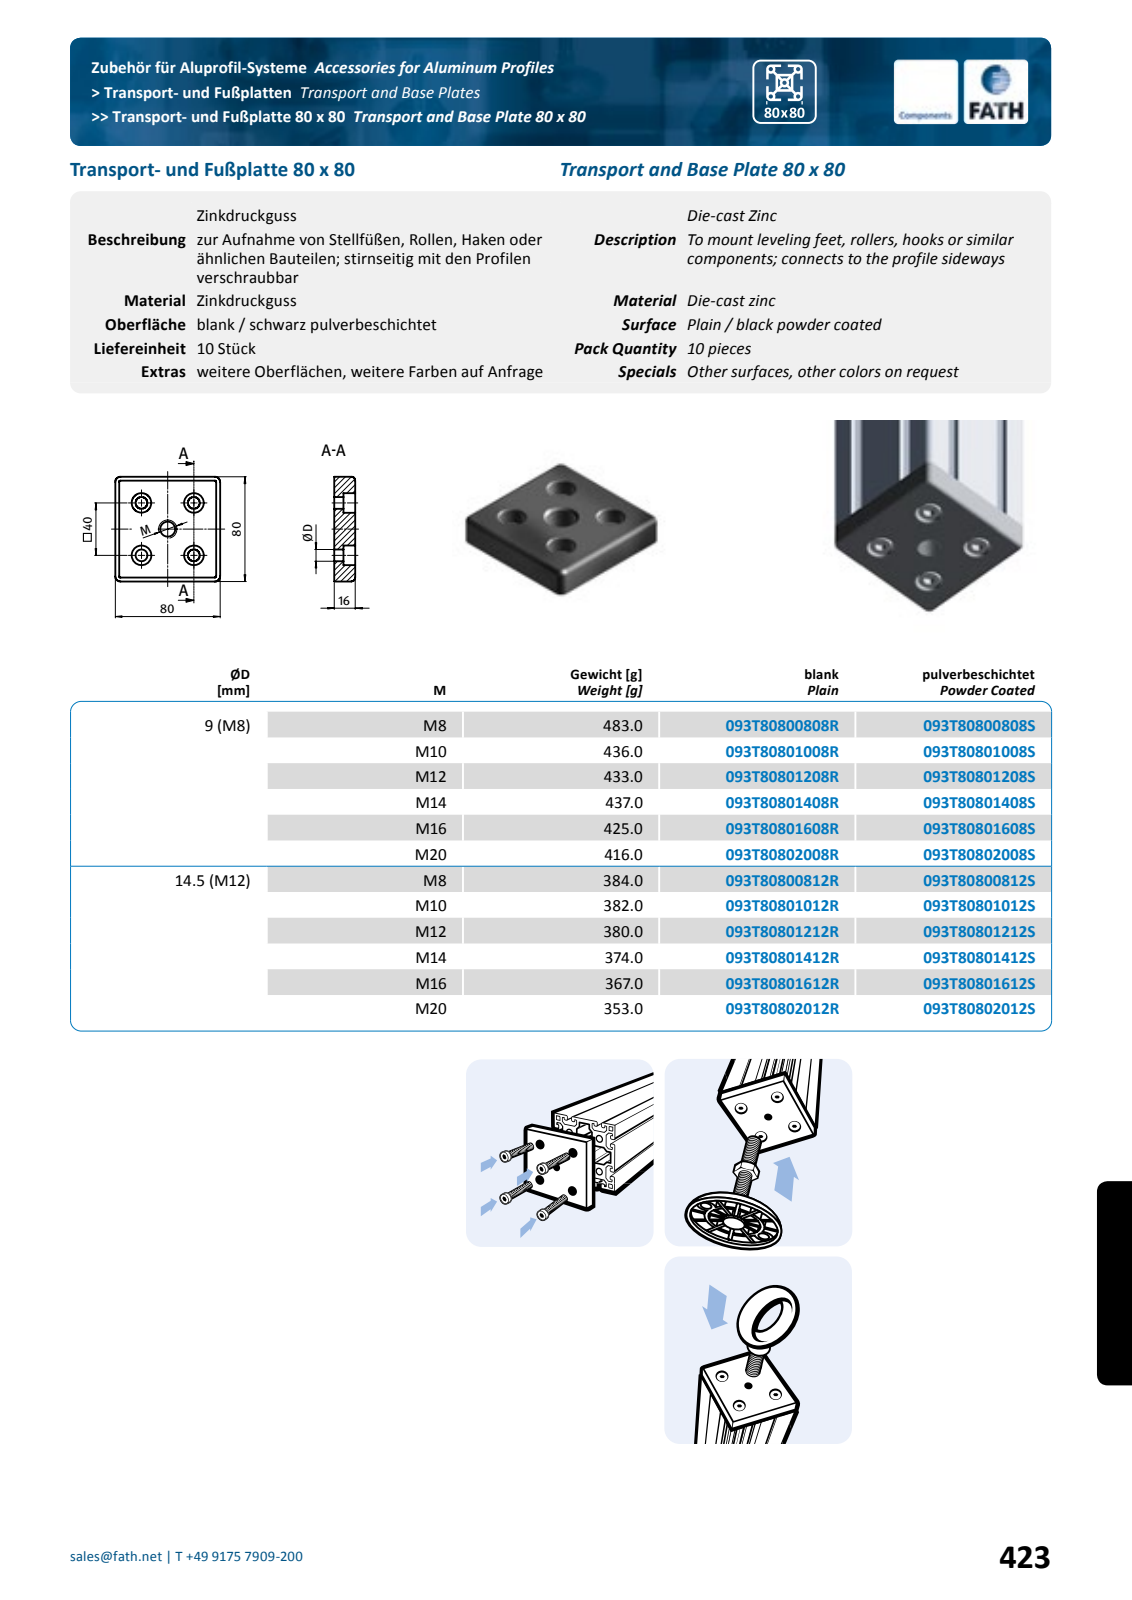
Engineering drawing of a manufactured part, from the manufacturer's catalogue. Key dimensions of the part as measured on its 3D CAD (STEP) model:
Part name (STEP PRODUCT): fath_093t80801208s
STEP written by: Spatial InterOp 3D (automotive_design)
Units: millimetres
Bodies: 1 solid, 280 faces (50 planar, 142 cylindrical, 88 other)
Overall size (bounding box): 80 × 80 × 16
Volume: 58 949 mm³ · Surface area: 29 165 mm²
Round holes (diameter × count): ⌀9 ×4, ⌀15 ×4, ⌀10.2 ×1
Round bosses / shafts (diameter × count): ⌀21 ×4
Partial cylindrical surfaces — rounded edges, fillets, slot ends (radius × count): R1 ×51, R0.5 ×8, R3 ×4, R4 ×4, R15 ×1
Main face-to-face distances: 4, 16, 3, 77, 12, 80, 38, 42, 35, 39
Hole centre spacings: 28.28, 40, 56.57
